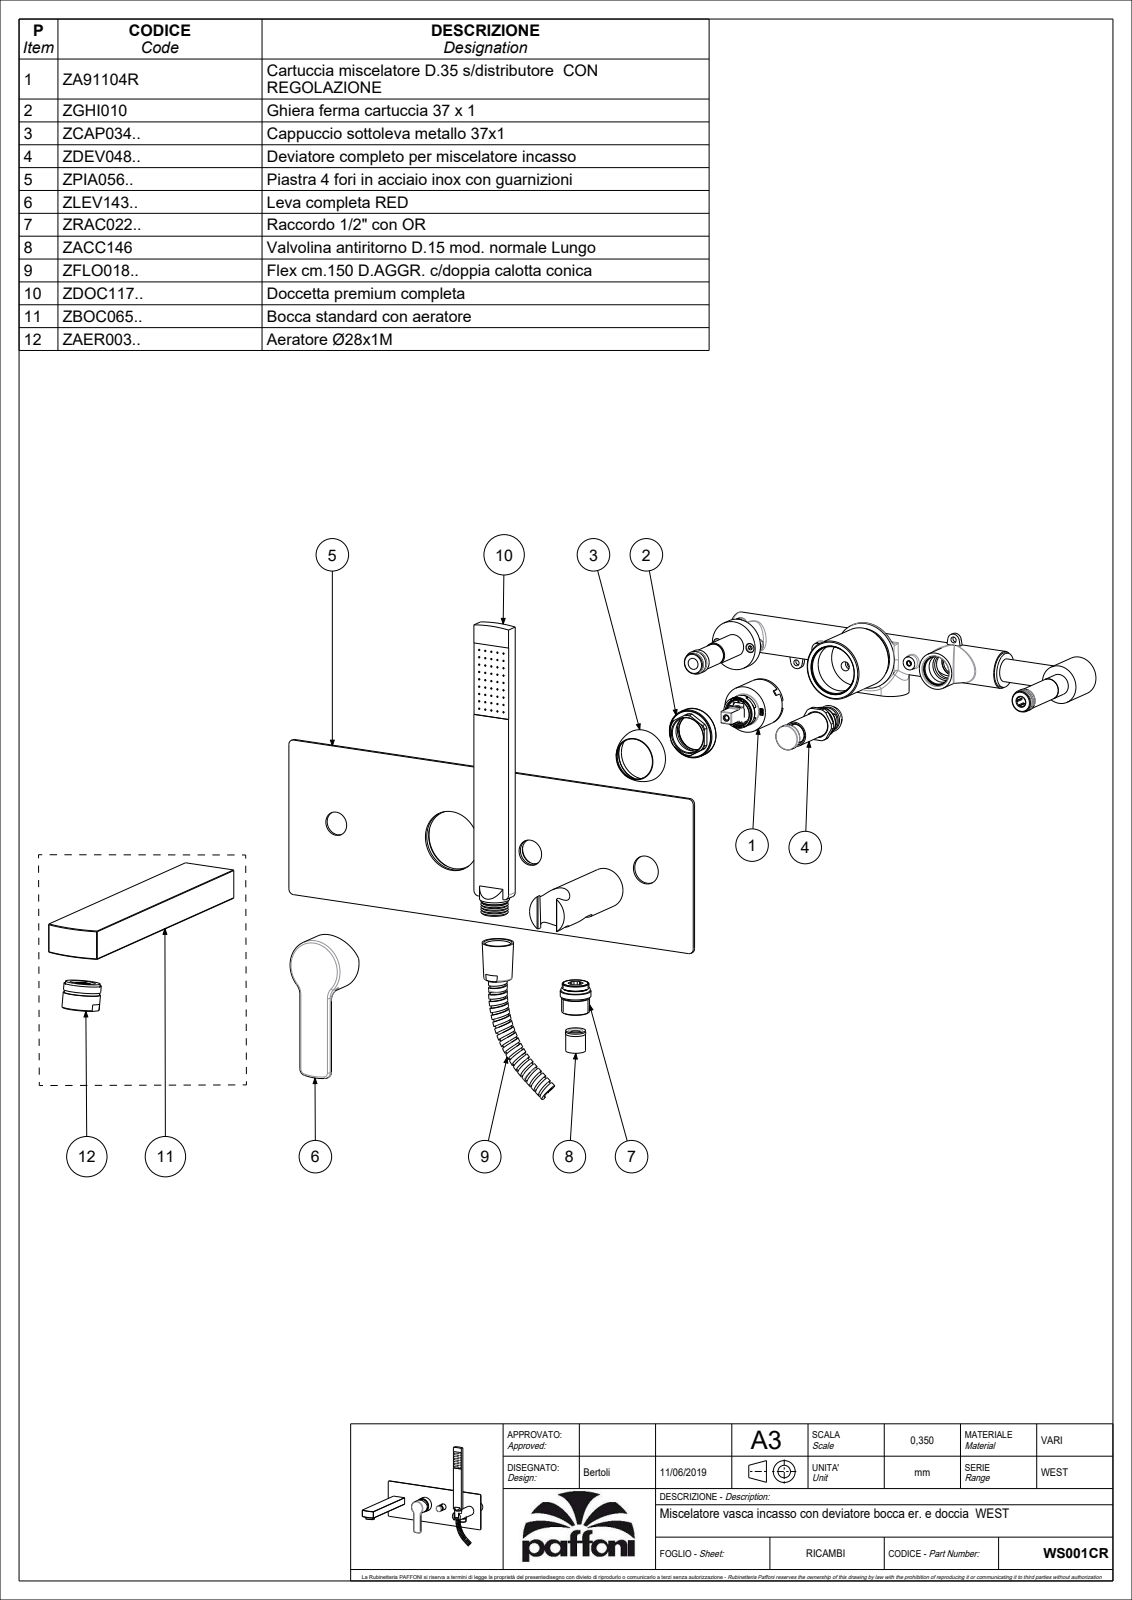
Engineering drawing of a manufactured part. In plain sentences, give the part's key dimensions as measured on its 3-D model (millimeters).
The part is named "WS001CR". Its 3-D file was written by "CREO PARAMETRIC BY PTC INC, 2020044 (CONFIG_CONTROL_DESIGN)". It is 8 solids with 3103 faces: 2381 planar, 382 cylindrical and 340 other. Overall it measures 356.89 by 329.3 by 210.25 millimeters. Its volume is 413 631 cubic millimeters and its surface area 221 076 square millimeters. Round holes: 2 of diameter 3.3, 2 of diameter 4, 2 of diameter 4.5, 2 of diameter 8.5, 2 of diameter 16, 2 of diameter 17.3, 2 of diameter 19, 2 of diameter 19.5, 1 of diameter 3, 1 of diameter 5, 1 of diameter 7.5, 1 of diameter 8. Round bosses or shafts: 11 of diameter 2, 2 of diameter 22, 1 of diameter 44.8, 1 of diameter 43, 1 of diameter 35, 1 of diameter 30, 1 of diameter 28, 1 of diameter 26.5. Partial cylindrical surfaces (rounded edges, fillets, slot ends): 45 of radius 0.5, 11 of radius 0.15, 6 of radius 4, 4 of radius 0.3, 4 of radius 1.5, 3 of radius 10, 2 of radius 1, 2 of radius 2.25. The main face-to-face distances are 2, 22, 73.5, 71.5, 10, 83.5, 81.5, 42, 1, 3. The hole center spacings are 100, 168, 3.5, 12.5, 40, 68, 99.8, 100.06.
